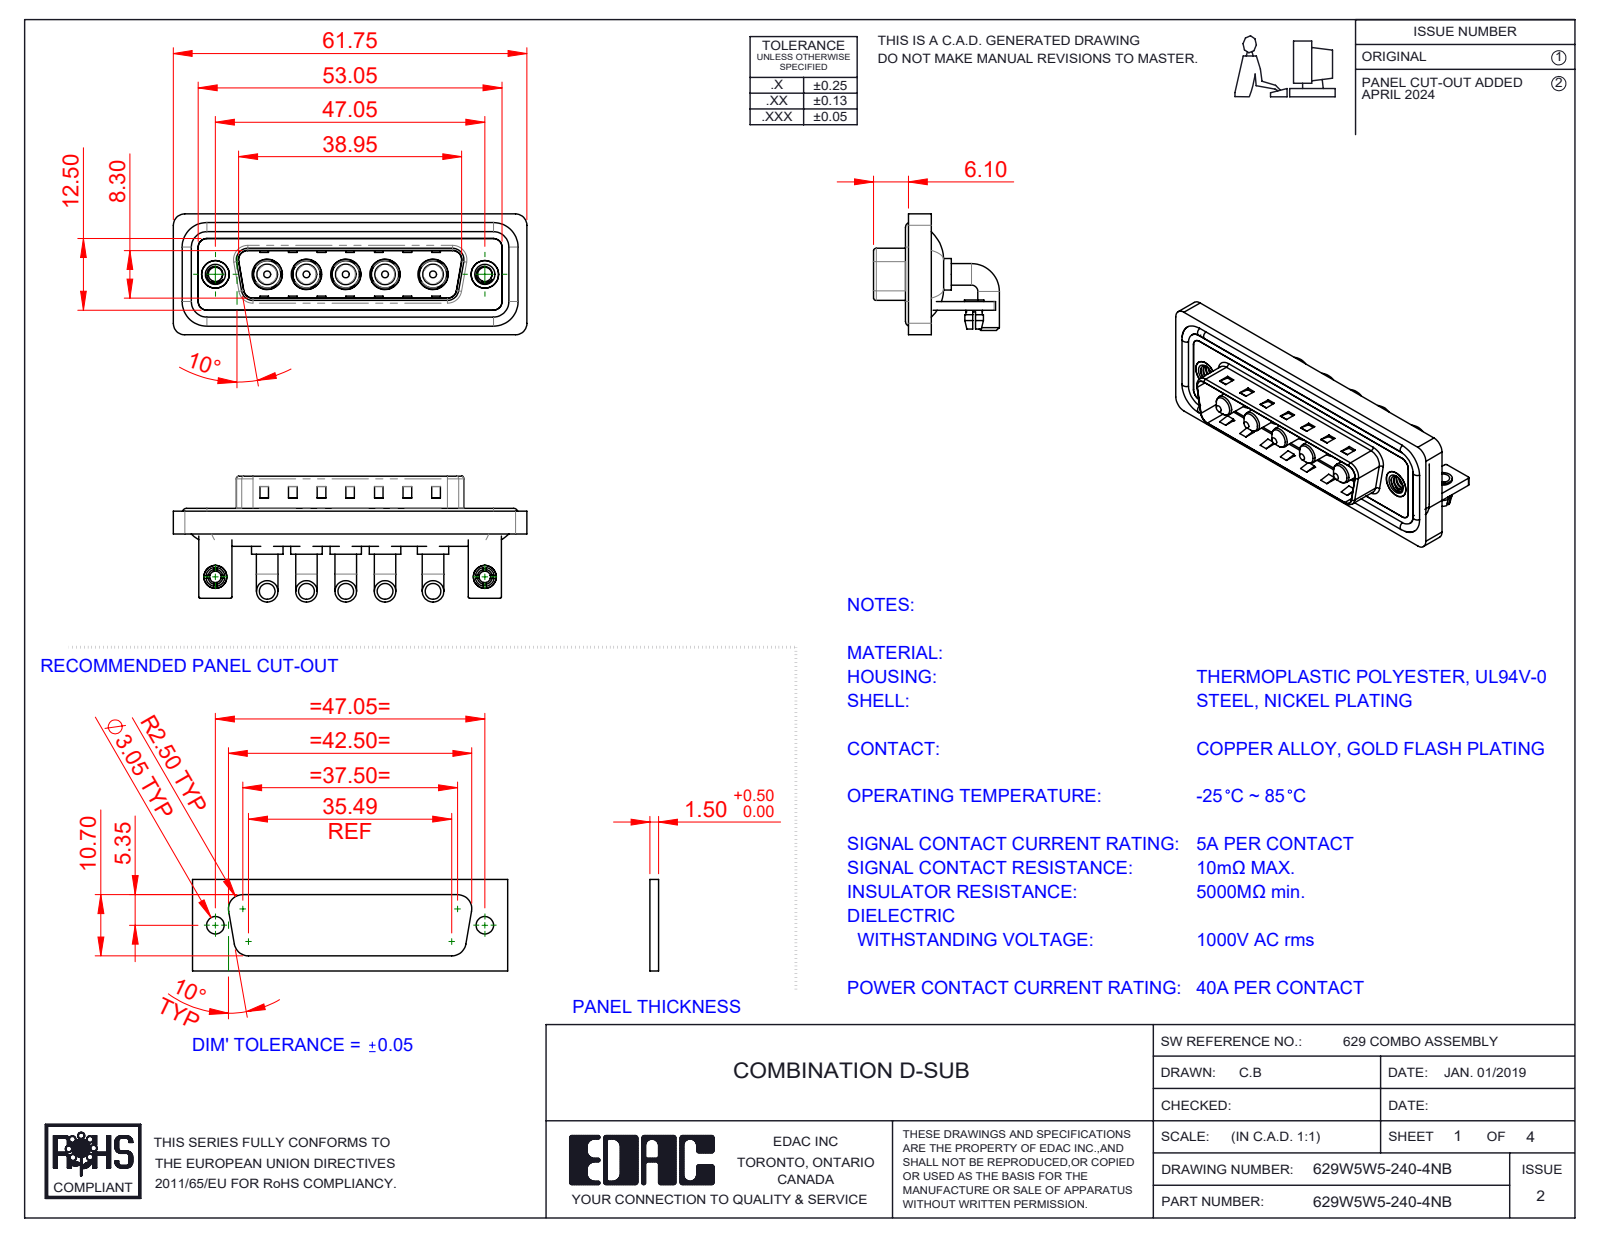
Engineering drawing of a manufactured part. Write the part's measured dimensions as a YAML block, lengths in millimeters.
part_name: "629Combo Shell Front_25 Contacts; 629Combo Shell Rear_25 Contacts; 629Combo Board Lock; Power Pin_40A RA (+5 more)"
step_written_by: "SolidWorks 2023 (CONFIG_CONTROL_DESIGN)"
units: millimeters
bodies: {solids: 21, faces: 828, planar: 327, cylindrical: 343, other: 158}
overall_size: [61.75, 21.98, 21.1]
volume: 8475
surface_area: 13290
round_holes:
  - {diameter: 4.85, count: 5}
  - {diameter: 5.3, count: 5}
  - {diameter: 2.5, count: 4}
  - {diameter: 2, count: 2}
  - {diameter: 3.2, count: 2}
  - {diameter: 4, count: 2}
  - {diameter: 4.8, count: 2}
  - {diameter: 5, count: 2}
round_bosses_or_shafts:
  - {diameter: 3.75, count: 10}
  - {diameter: 5.5, count: 5}
  - {diameter: 5.2, count: 5}
  - {diameter: 4.75, count: 5}
  - {diameter: 3.6, count: 5}
  - {diameter: 1.6, count: 4}
  - {diameter: 4.9, count: 2}
  - {diameter: 4, count: 2}
partial_cylinders:
  - {radius: 2, count: 19}
  - {radius: 1.5, count: 18}
  - {radius: 0.25, count: 16}
  - {radius: 0.5, count: 9}
  - {radius: 1.6, count: 8}
  - {radius: 2.1, count: 5}
  - {radius: 0.6, count: 4}
  - {radius: 0.65, count: 4}
face_to_face_distances: [0.4, 1.5, 2.9, 0.8, 2.1, 3.7, 1.1, 4.5, 4.1, 1.2]
hole_center_spacings: [6.86, 13.73, 47.05, 6.85, 6.87, 8.37, 8.38, 9.04]
